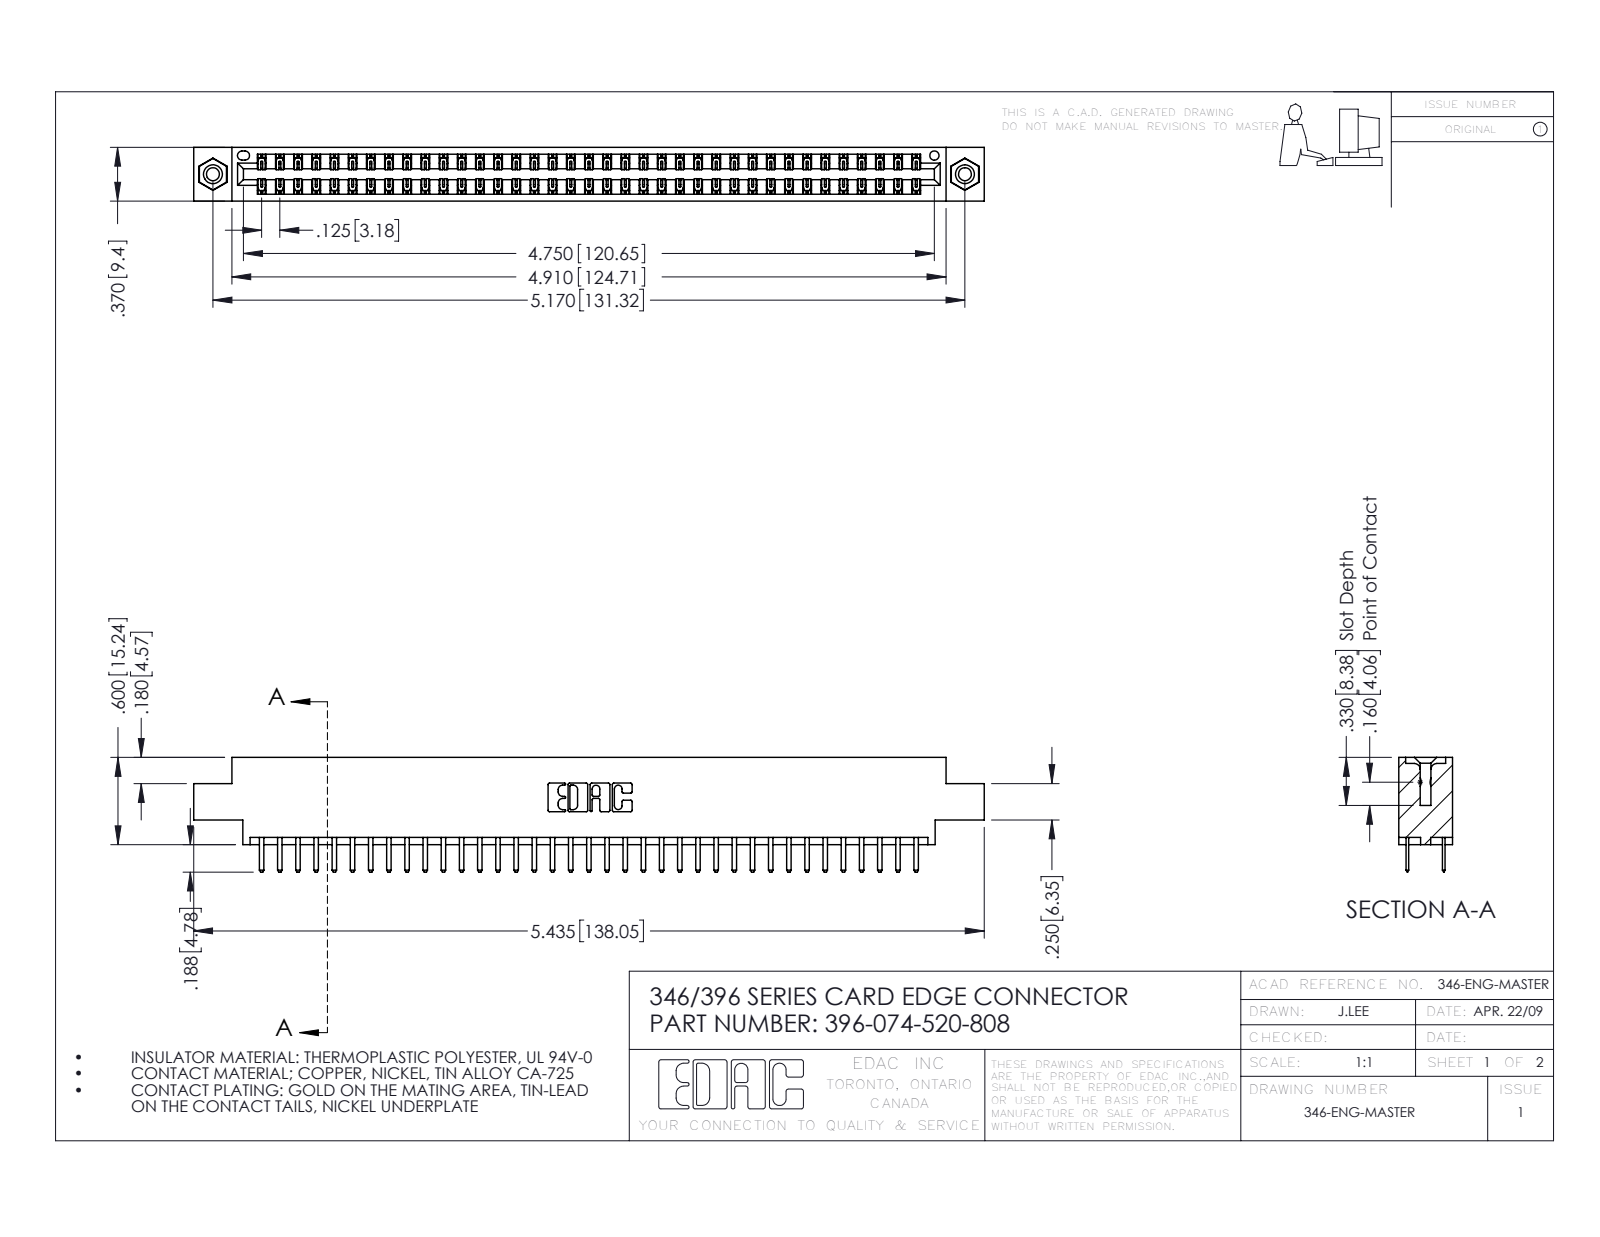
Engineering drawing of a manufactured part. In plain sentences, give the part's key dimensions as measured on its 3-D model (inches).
The part is named "345-292-001_345-293-120; 396-074-520-808; 346 Part_0.170 Offset - 0.156 Dia-TI; 345-250-001_345-250-003-102". Its 3-D file was written by "SolidWorks 2016 (CONFIG_CONTROL_DESIGN)". It is 77 solids with 4330 faces: 2850 planar, 1464 cylindrical and 16 other. Overall it measures 5.435 by 0.788 by 0.37 inches. Its volume is 0.807 cubic inches and its surface area 28.25 square inches. Round holes: 2 of diameter 0.089, 2 of diameter 0.125, 2 of diameter 0.156, 1 of diameter 0.064. Round bosses or shafts: 2 of diameter 0.155. Partial cylindrical surfaces (rounded edges, fillets, slot ends): 111 of radius 0.006, 78 of radius 0.01, 22 of radius 0.01, 6 of radius 0.007, 6 of radius 0.031, 3 of radius 0.026, 2 of radius 0.014, 2 of radius 0.022. The main face-to-face distances are 0.048, 0.322, 0.37, 0.25, 0.275, 0.072, 0.298, 0.025, 0.222, 0.148. The hole center spacings are 0.246, 4.961, 5.17.
